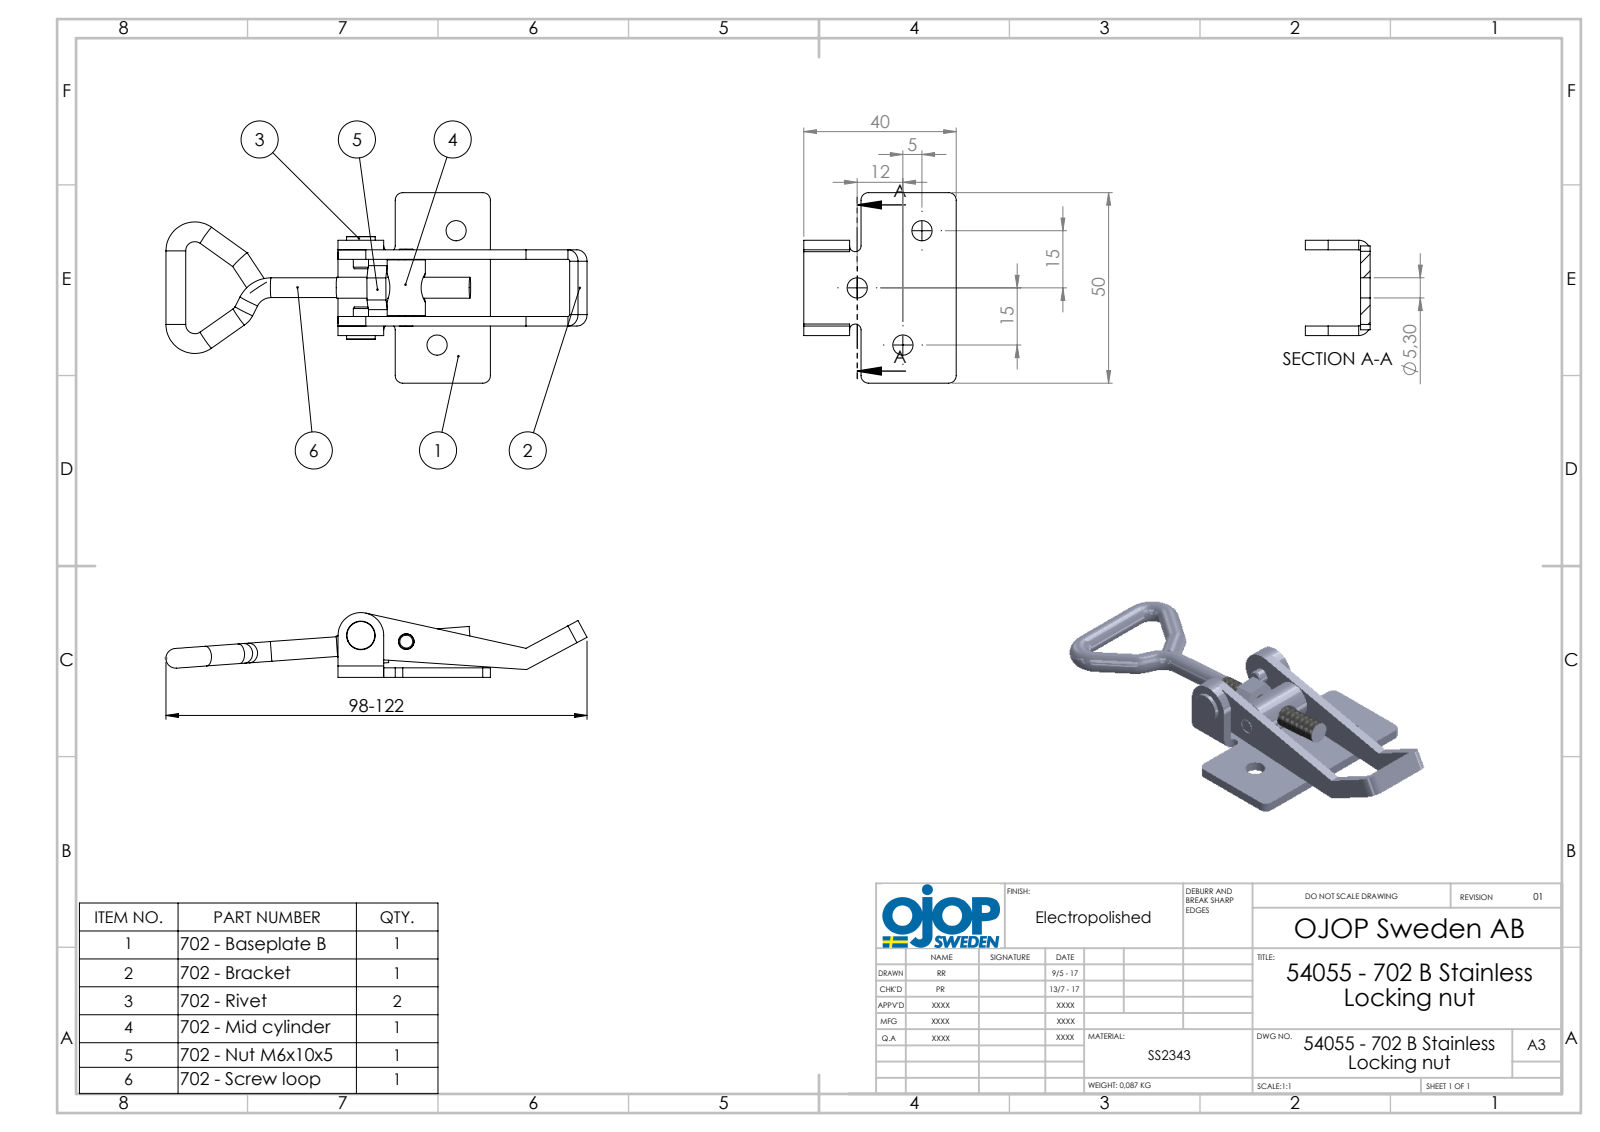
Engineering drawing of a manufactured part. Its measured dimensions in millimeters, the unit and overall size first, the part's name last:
Units: millimetres
Overall size (bounding box): 113.24 × 50 × 17
Round holes (diameter × count): ⌀5 ×3, ⌀5.3 ×3, ⌀4.1 ×2
Round bosses / shafts (diameter × count): ⌀5.18 ×6, ⌀4 ×2, ⌀10 ×1, ⌀7.5 ×1, ⌀6 ×1, ⌀5.5 ×1
Partial cylindrical surfaces — rounded edges, fillets, slot ends (radius × count): R0.5 ×4, R2 ×4, R3 ×4, R1.5 ×2, R6 ×1
Main face-to-face distances: 2.5, 17.5, 20, 15, 5, 22.5, 25, 12.5, 35, 32.5
Hole centre spacings: 12.03, 19.21, 22.67, 30.41
Volume: 11 834 mm³ · Surface area: 11 314 mm²
Bodies: 7 solids, 164 faces (65 planar, 73 cylindrical, 26 other)
Part name (STEP PRODUCT): 54055 - 702 B Stainless Locking nut; 702 - B; 702 - Bygel; 702 - Ansatsnit (+3 more)
STEP written by: SolidWorks 2015 (AUTOMOTIVE_DESIGN)
